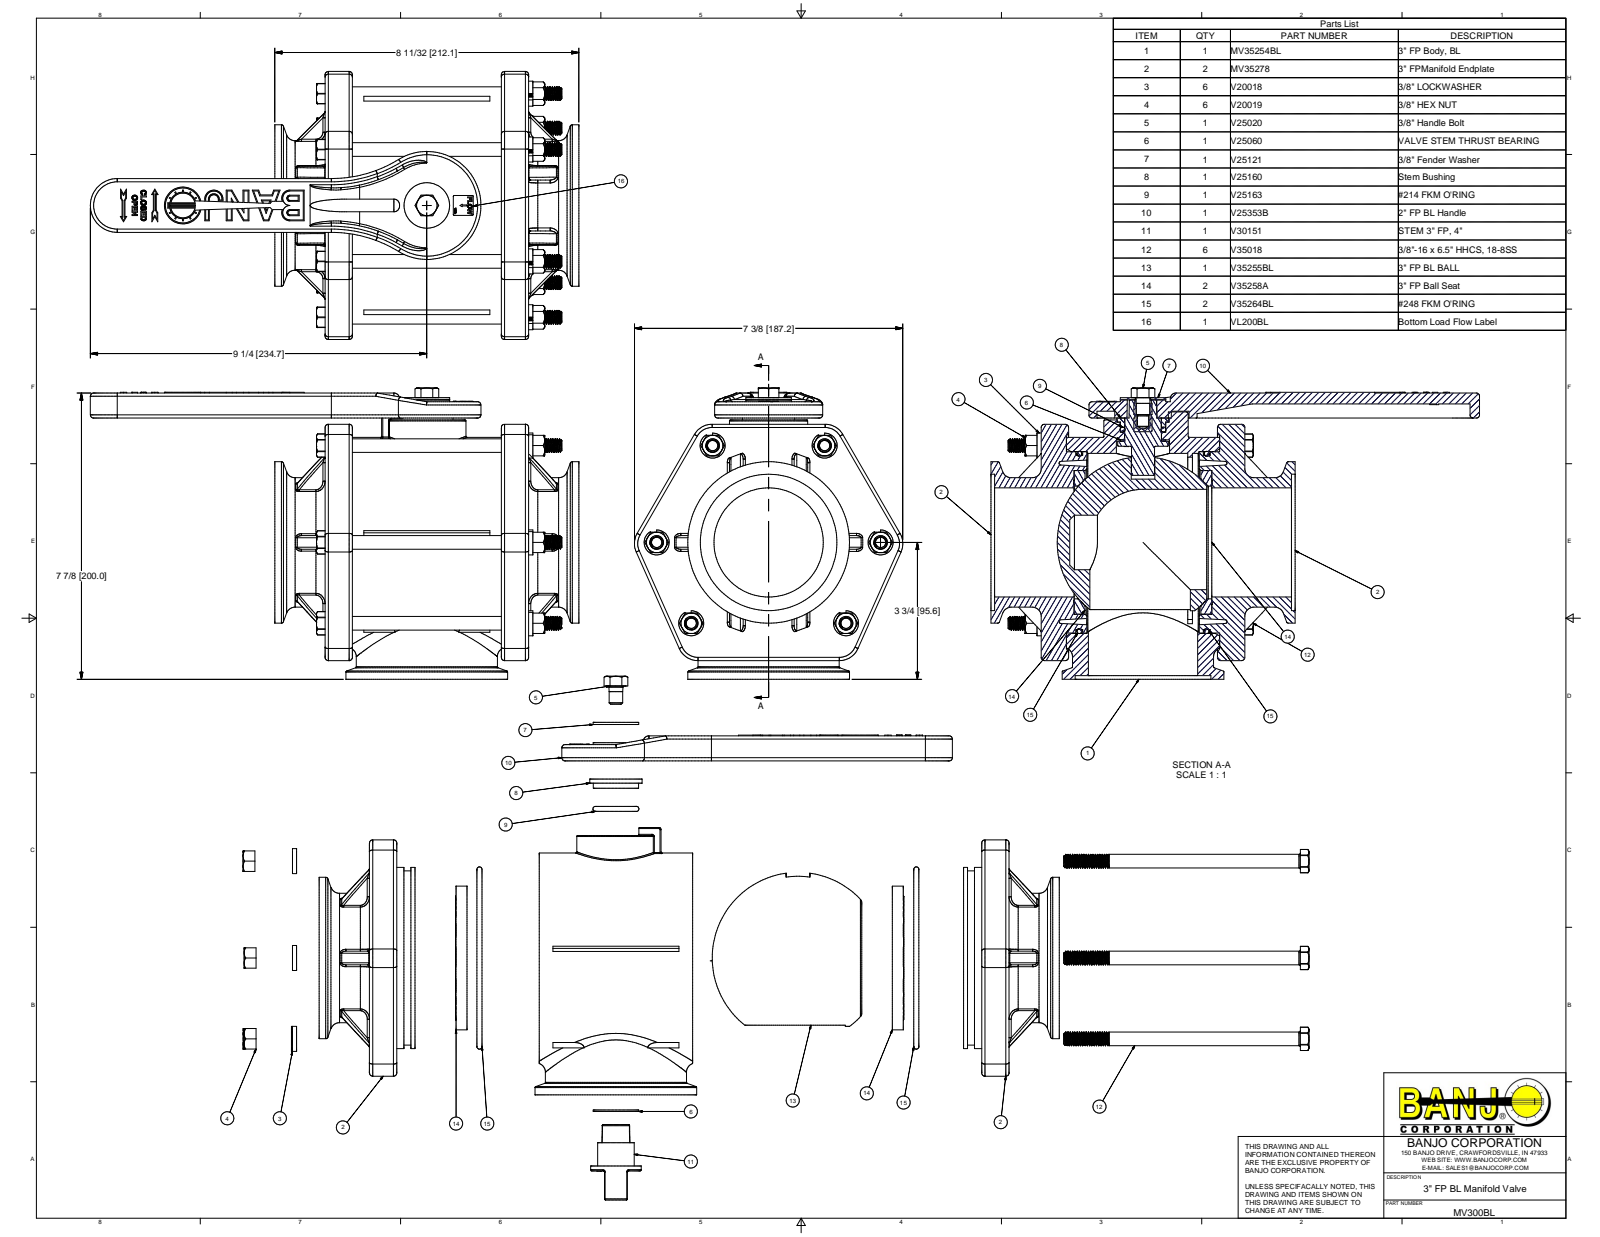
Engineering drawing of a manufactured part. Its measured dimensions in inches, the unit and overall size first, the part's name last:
Units: inches
Overall size (bounding box): 13.415 × 8.012 × 7.37
Round holes (diameter × count): ⌀0.44 ×8, ⌀0.307 ×6, ⌀0.385 ×6, ⌀2.92 ×2, ⌀3 ×2, ⌀0.307 ×1, ⌀0.375 ×1, ⌀0.406 ×1, ⌀0.681 ×1, ⌀0.962 ×1, ⌀1 ×1, ⌀1.016 ×1
Round bosses / shafts (diameter × count): ⌀0.687 ×6, ⌀0.375 ×6, ⌀0.294 ×6, ⌀4.44 ×2, ⌀5.78 ×1, ⌀4.985 ×1, ⌀4.793 ×1, ⌀3.875 ×1
Partial cylindrical surfaces — rounded edges, fillets, slot ends (radius × count): R0.09 ×32, R0.06 ×25, R0.03 ×10, R0.032 ×10, R0.155 ×8, R0.32 ×6, R0.563 ×6, R0.031 ×4
Main face-to-face distances: 0.69, 4.9, 5.59, 0.905, 4.685, 0.215, 3.995, 0.06, 0.75, 4.84
Hole centre spacings: 3.075, 3.075, 2.417, 4.92, 4.25, 5.326, 5.655, 5.656
Volume: 139.1 in³ · Surface area: 803.9 in²
Bodies: 35 solids, 1971 faces (766 planar, 552 cylindrical, 653 other)
Part name (STEP PRODUCT): MV35254BLX; MV35254BL; MV35278X; MV35278 (+8 more)
STEP written by: Autodesk Inventor 2016 (AUTOMOTIVE_DESIGN)
